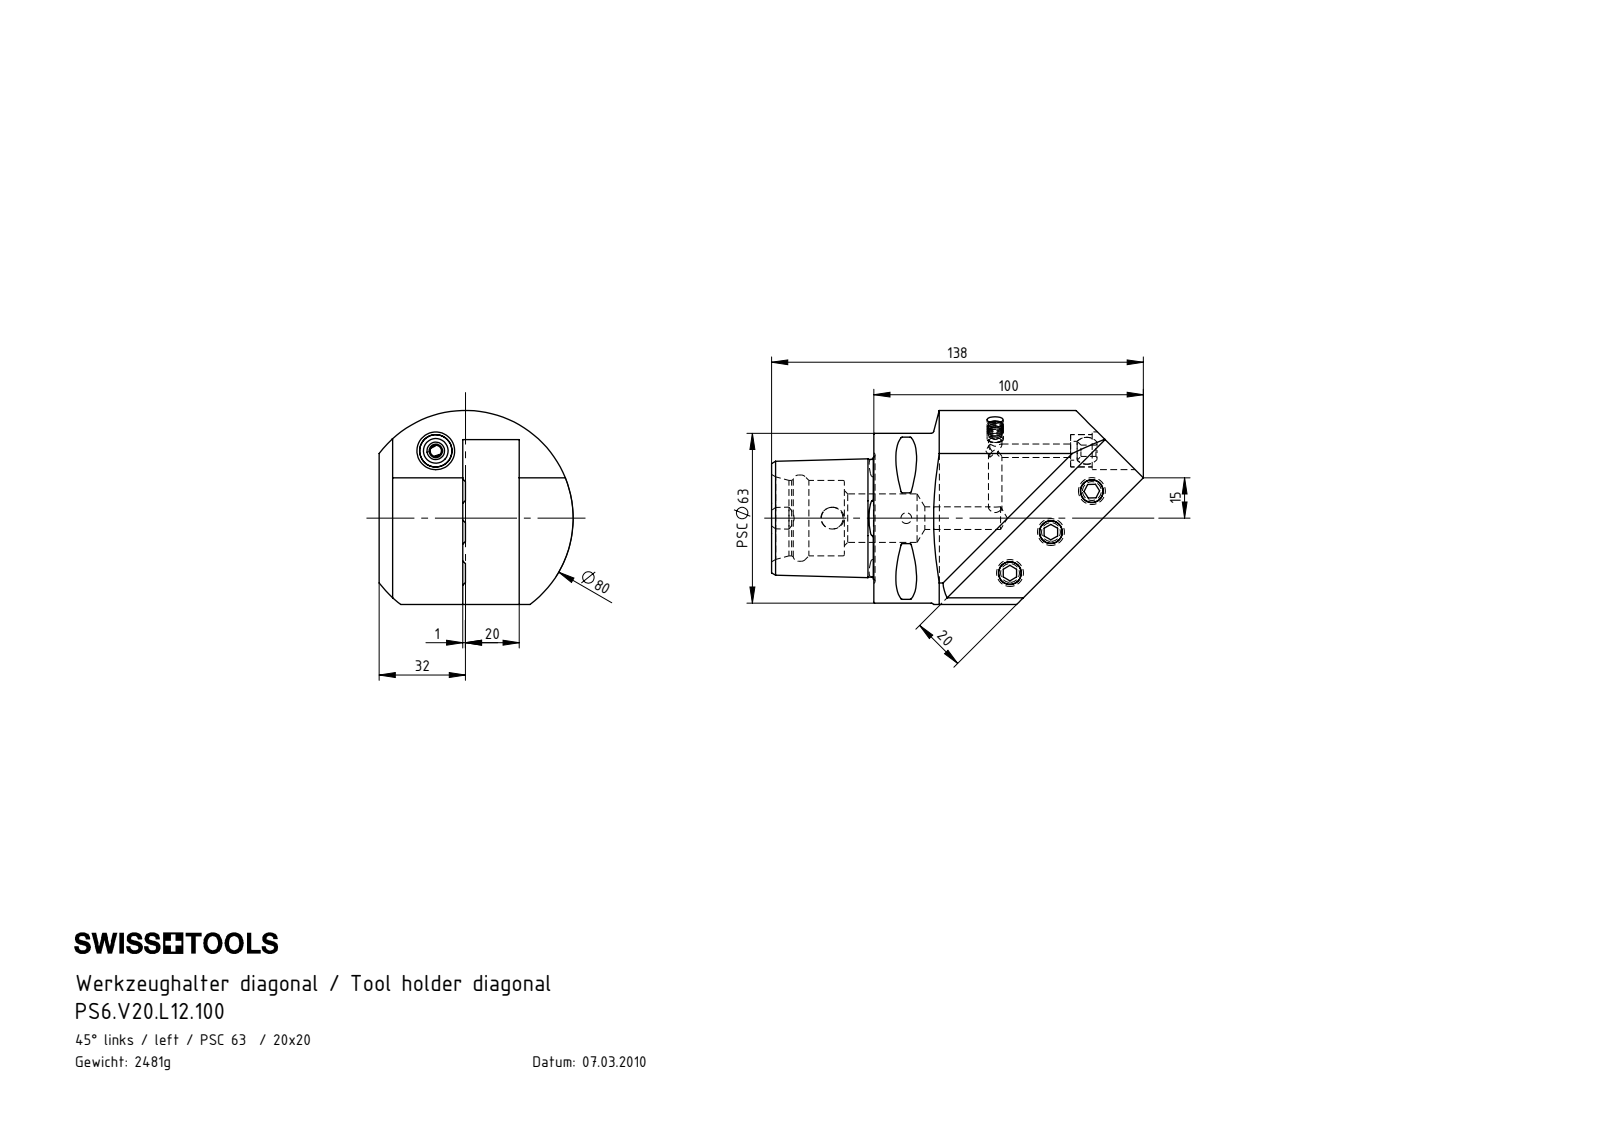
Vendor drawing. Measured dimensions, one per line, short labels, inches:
name: KU1-U12.001.010_1; PS6-V20.L12.100_A; KVT_MB_600_060; ISO 4026 - M10 x 25 (+3 more)
written by: SolidWorks 2012 (CONFIG_CONTROL_DESIGN)
unit: in
bodies: 8 solids, 258 faces (62 planar, 68 cylindrical, 128 other)
size: 5.433 × 2.835 × 2.835
volume: 19.3 in³; area: 73.67 in²
holes: 3× ⌀0.197, 3× ⌀0.335, 1× ⌀0.157, 1× ⌀0.165, 1× ⌀0.236, 1× ⌀0.276, 1× ⌀0.319, 1× ⌀0.331, 1× ⌀0.472, 1× ⌀0.551, 1× ⌀0.709, 1× ⌀1.102
bosses: 3× ⌀0.394, 1× ⌀2.48, 1× ⌀0.236
rounds: 8× R0.02, 1× R0.236, 1× R1.575
face distances: 0.787, 0.197, 0.827, 1.85, 1.024, 2.047, 1.22, 1.496, 1.063, 0.98
hole spacings: 0.846, 0.847, 1.075, 1.083, 1.693, 1.715, 2.124, 2.719
